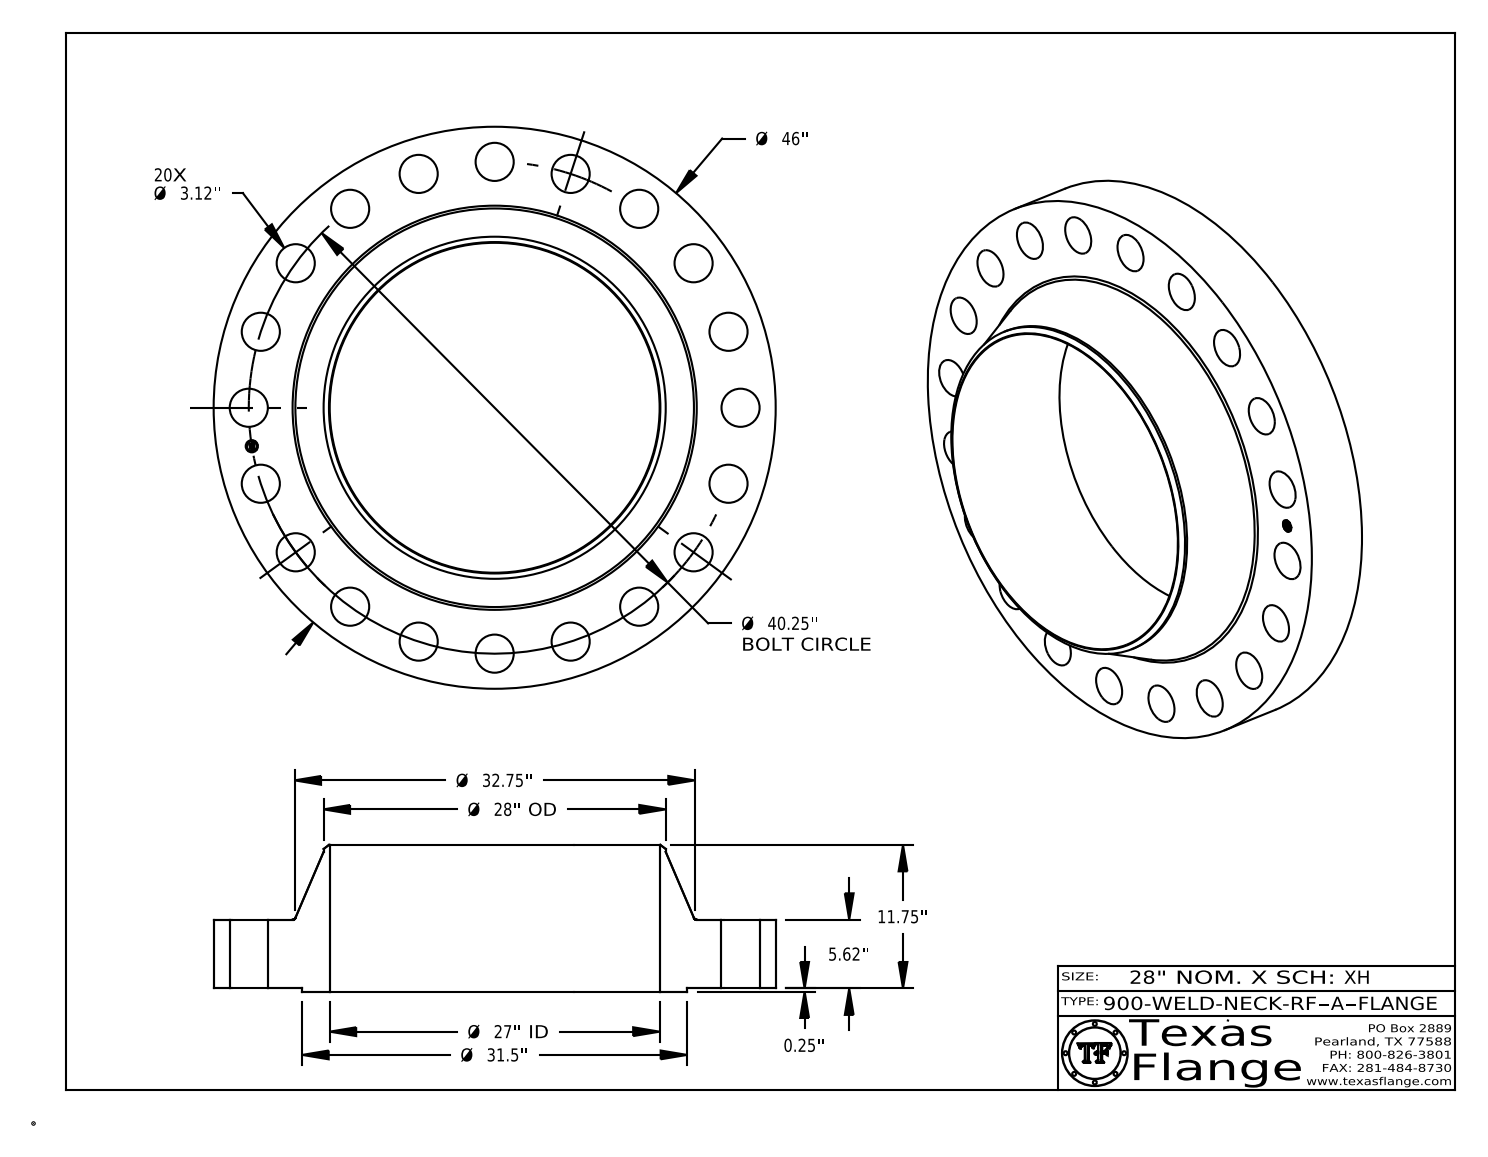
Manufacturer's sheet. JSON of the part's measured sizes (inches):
{"part_name": "900-WELD-NECK-RF, Series A", "step_written_by": "CATIA V5 STEP AP214 (AUTOMOTIVE_DESIGN)", "units": "inches", "bodies": {"solids": 1, "faces": 443, "planar": 369, "cylindrical": 68, "other": 6}, "overall_size": [46, 46, 12], "volume_in3": 6187, "surface_area_in2": 5206, "round_holes": [[3.12, 20], [1, 1], [27, 1]], "round_bosses_or_shafts": [[0.061, 8], [46, 1], [31.5, 1], [28, 1], [0.788, 1]], "face_to_face_distances": [5.62, 0.25, 5.87, 12, 11.75, 6.13, 5.855, 5.605, 0.015, 6.145], "hole_center_spacings": [6.296, 32.563, 35.863, 28.461, 39.755, 12.438, 18.273, 20.125]}
